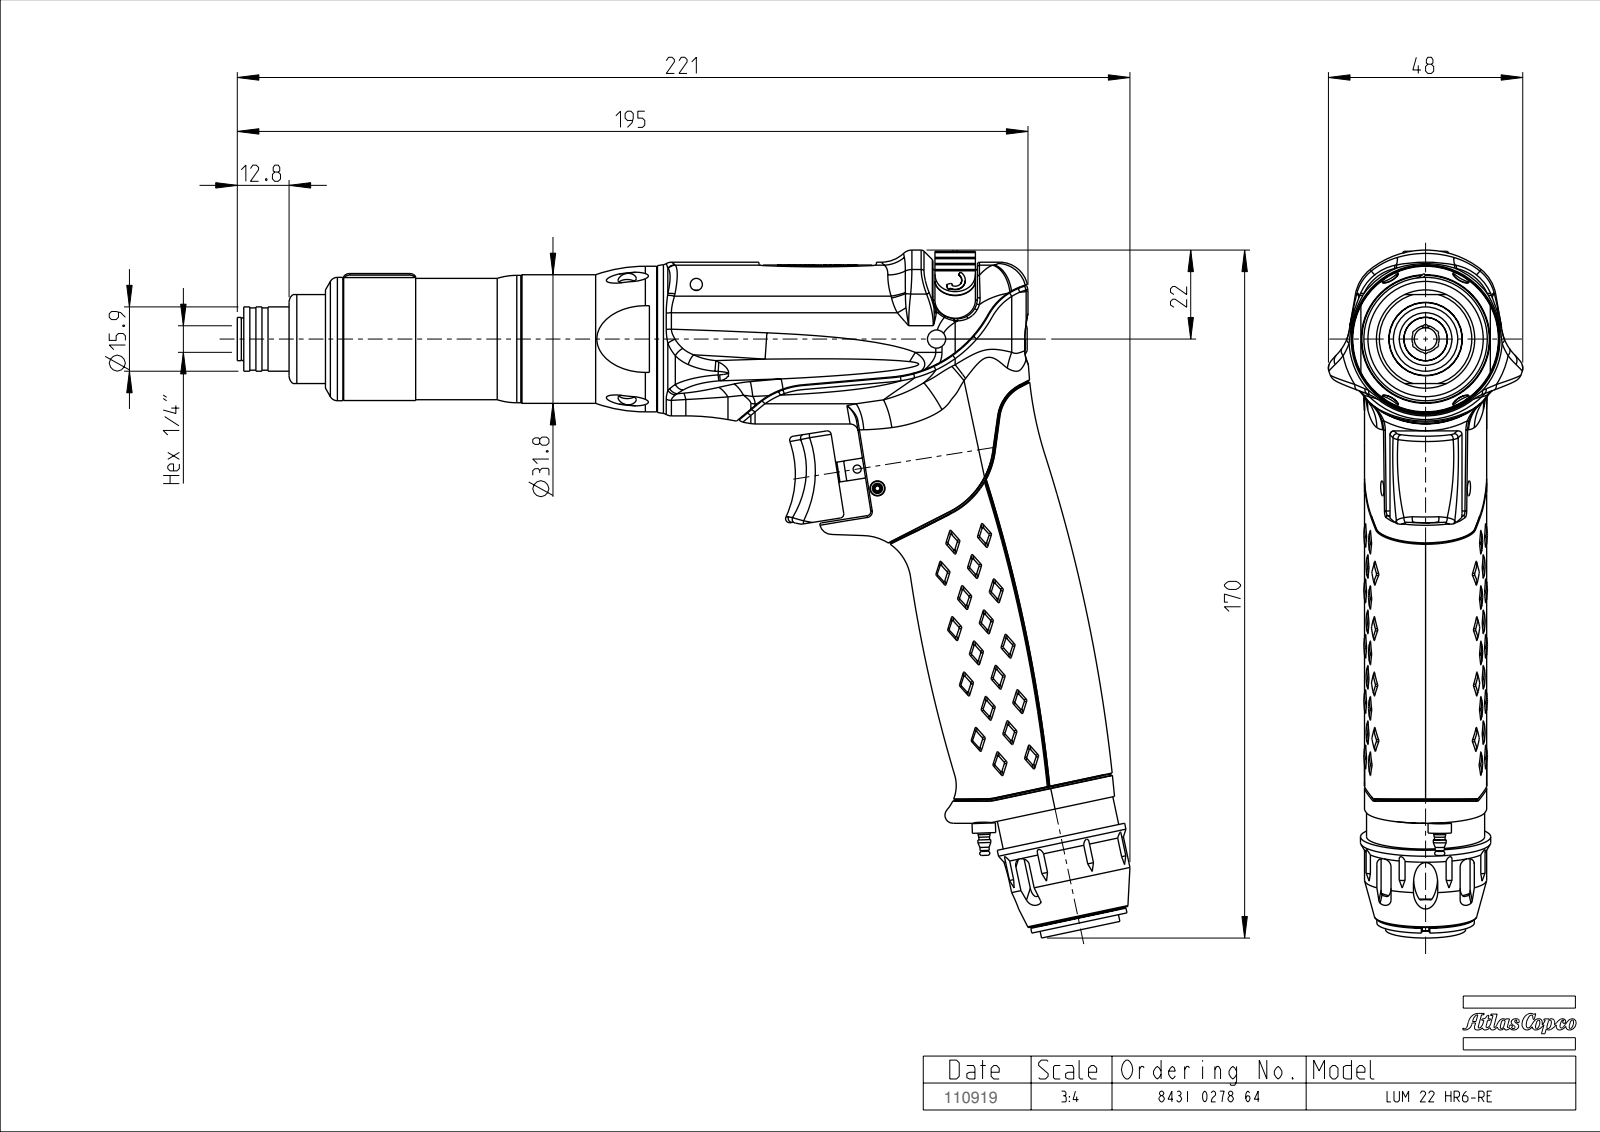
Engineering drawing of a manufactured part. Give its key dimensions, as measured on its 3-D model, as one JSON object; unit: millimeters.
{"part_name": "TMP163749_SW", "step_written_by": "PRO/ENGINEER BY PARAMETRIC TECHNOLOGY CORPORATION, 2008310 (CONFIG_CONTROL_DESIGN)", "units": "millimeters", "bodies": {"solids": 0, "faces": 838, "planar": 89, "cylindrical": 174, "other": 575}, "overall_size": [220.69, 170.1, 48.06], "round_holes": [[4.5, 2], [3, 1], [7.5, 1], [11.4, 1], [11.45, 1], [26.4, 1]], "round_bosses_or_shafts": [[36, 1], [32.2, 1], [31.8, 1], [31.5, 1], [30.5, 1], [30.4, 1], [30.2, 1], [30, 1]], "partial_cylinders_radius": [[1, 9], [0.75, 8], [10, 4], [38, 3], [2.5, 2], [3, 2], [5, 2], [5.5, 2]], "face_to_face_distances": [1.5, 29.8, 32, 27.29, 57.09, 3.2, 30.49, 60.29, 1.7, 28.79]}
